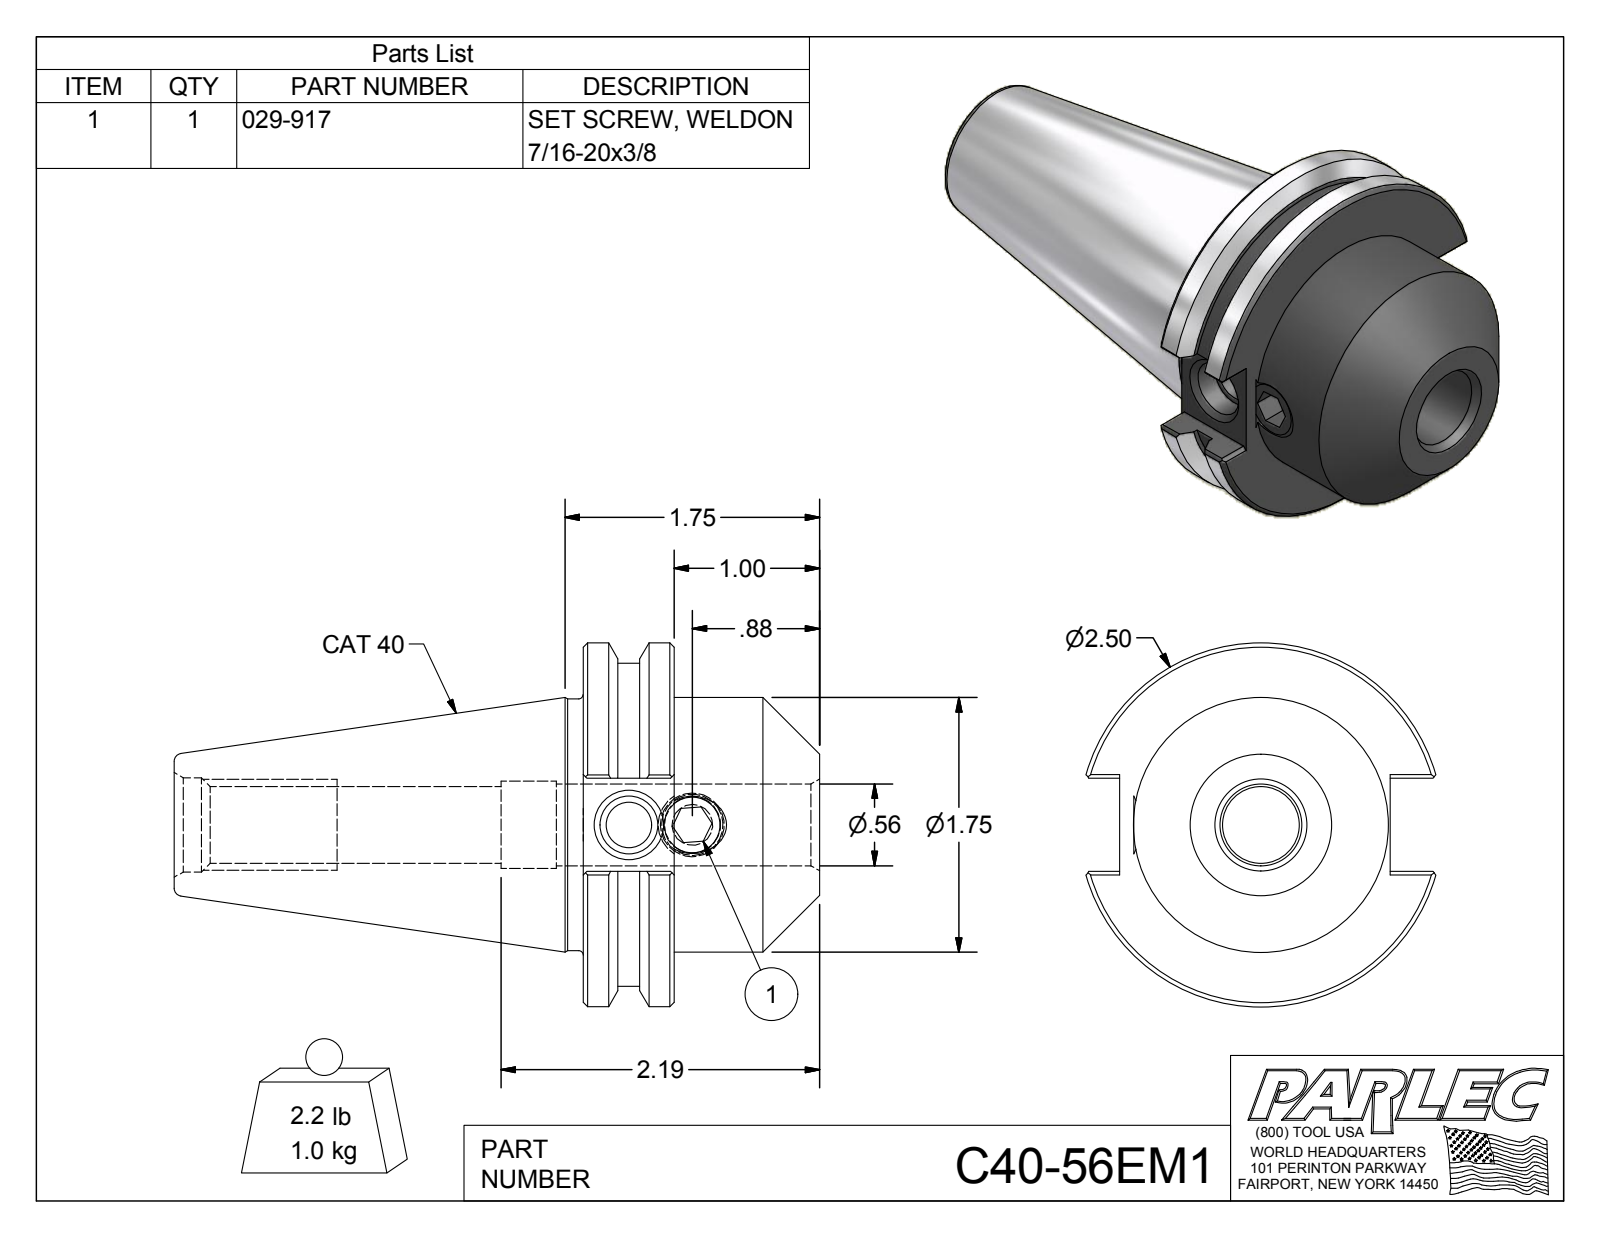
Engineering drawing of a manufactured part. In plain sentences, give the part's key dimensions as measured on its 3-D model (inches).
The part is named "C40-56EM1; C40-56EM1-1; 029-917". Its 3-D file was written by "Autodesk Inventor 2012 (AUTOMOTIVE_DESIGN)". It is 2 solids with 80 faces: 43 planar, 16 cylindrical and 21 other. Overall it measures 4.438 by 2.5 by 2.403 inches. Its volume is 7.841 cubic inches and its surface area 38.87 square inches. Round holes: 1 of diameter 0.315, 1 of diameter 0.383, 1 of diameter 0.396, 1 of diameter 0.527, 1 of diameter 0.563, 1 of diameter 0.6, 1 of diameter 0.648. Round bosses or shafts: 1 of diameter 2.5, 1 of diameter 2.219, 1 of diameter 1.75, 1 of diameter 1.73, 1 of diameter 0.437. The main face-to-face distances are 0.625, 1.625, 1, 0.236, 0.64, 1.86, 2.812, 3.437, 4.437, 3.201. The hole center spacings are 0.435.
